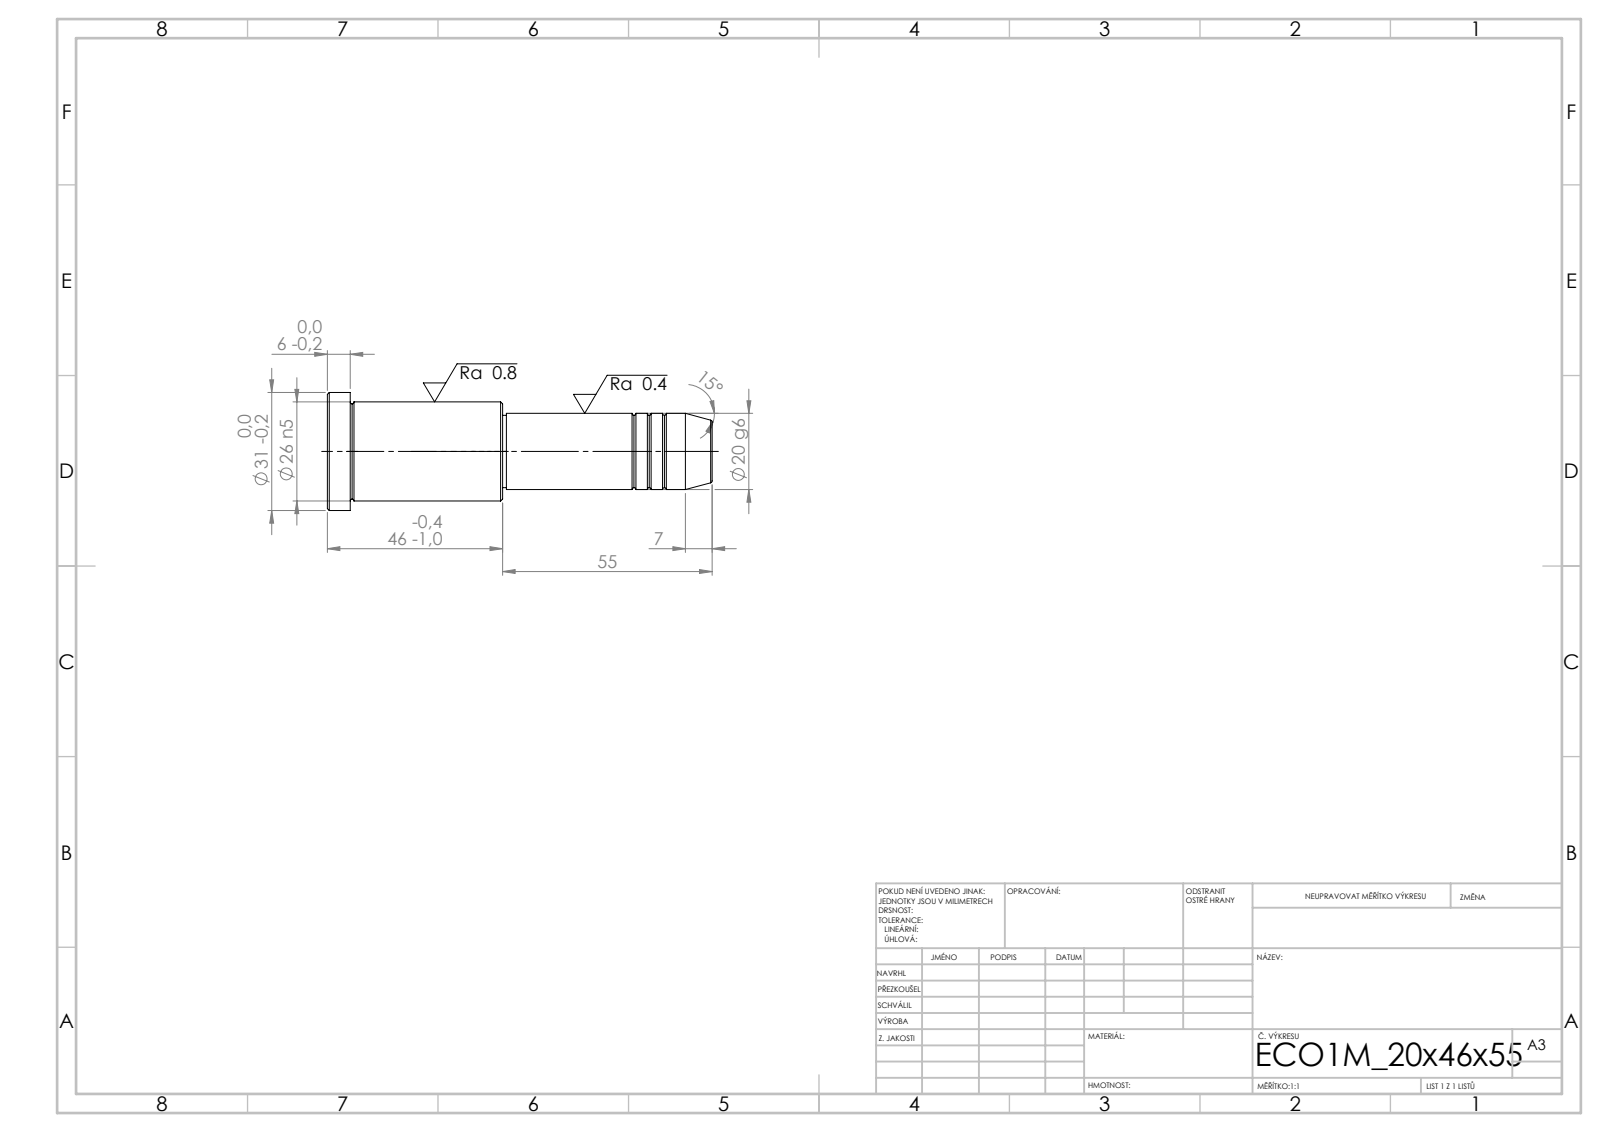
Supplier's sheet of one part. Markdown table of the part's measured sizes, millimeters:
| quantity | value |
| --- | --- |
| STEP written by | SolidWorks 2019 (CONFIG_CONTROL_DESIGN) |
| units | millimeters |
| bodies | 1 solid, 43 faces (5 planar, 14 cylindrical, 24 other) |
| overall size | 101 × 31 × 31 |
| volume | 42 500 mm³ |
| surface area | 8 824 mm² |
| round bosses / shafts (diameter × count) | 31 × 1, 26 × 1, 20 × 1, 19 × 1 |
| main face-to-face distances | 6, 40, 46, 55, 95, 101, 54, 1, 41, 47 |
